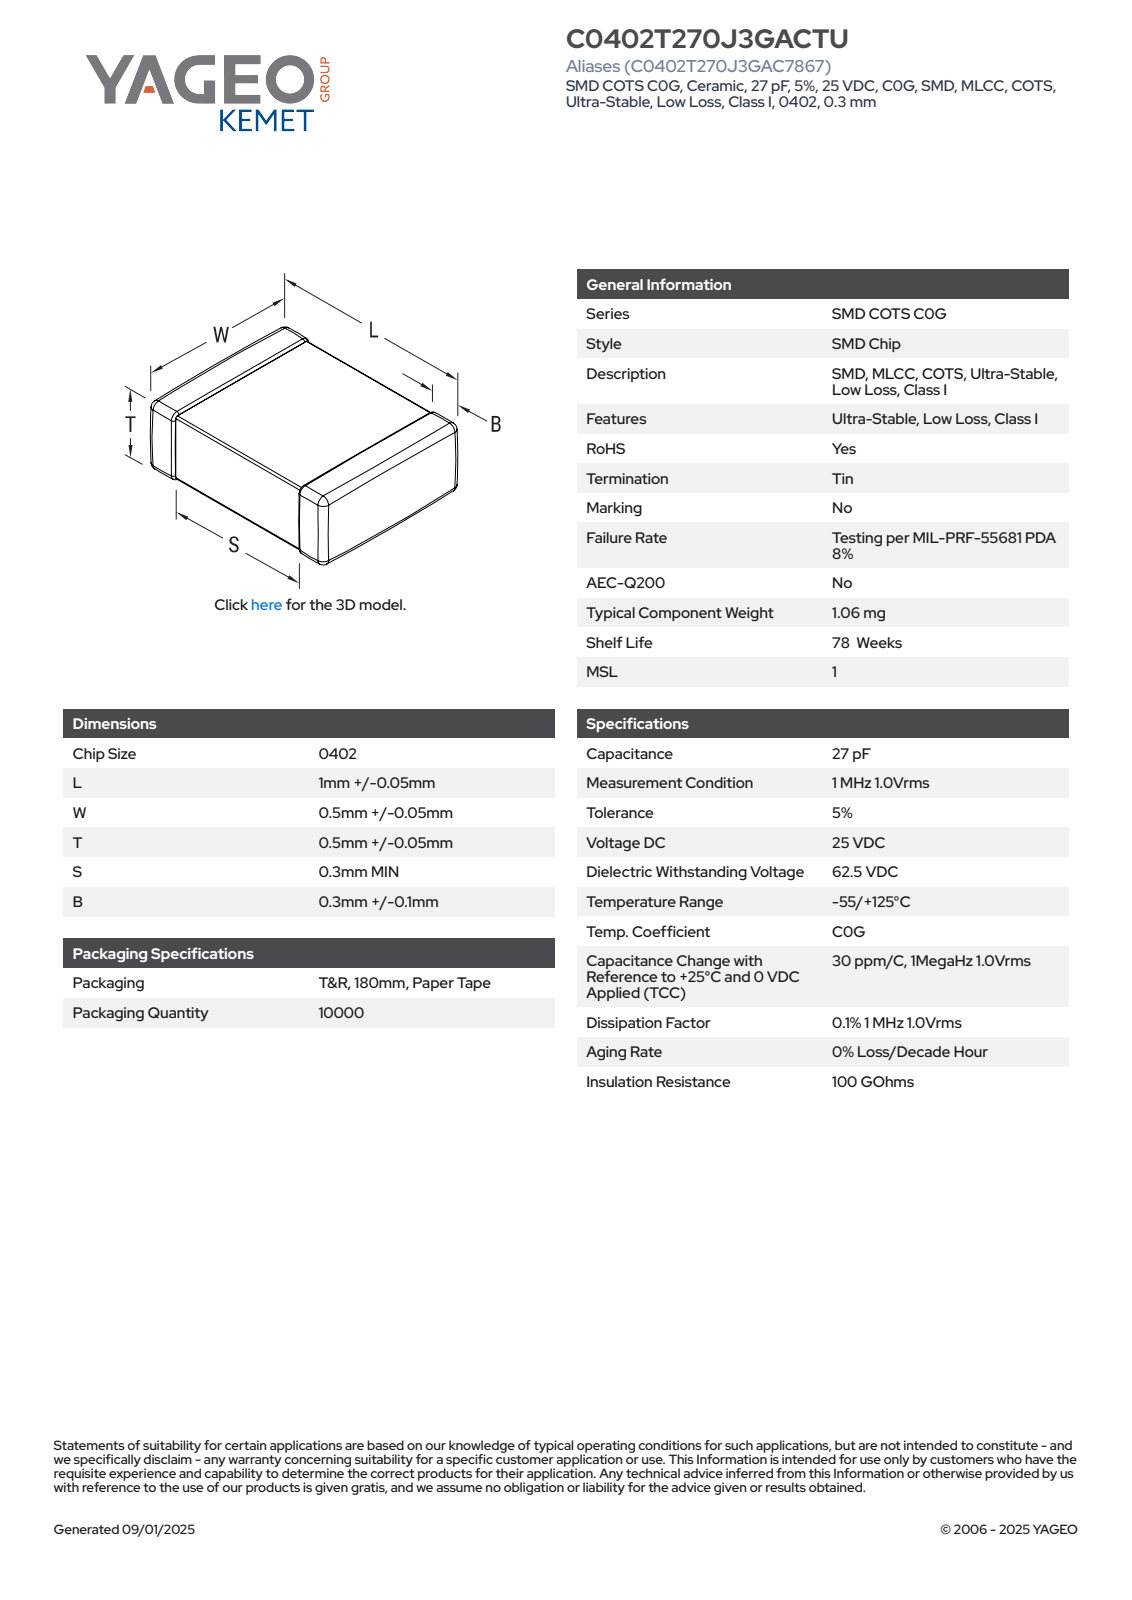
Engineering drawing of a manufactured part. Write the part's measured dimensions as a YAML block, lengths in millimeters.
part_name: "CCSM_STD_0402_L1.05W0.55T0.55B0.4"
step_written_by: "SolidWorks 2014 (AUTOMOTIVE_DESIGN)"
units: millimeters
bodies: {solids: 4, faces: 129, planar: 71, cylindrical: 42, other: 16}
overall_size: [1.05, 0.55, 0.55]
volume: 0.311
surface_area: 3
face_to_face_distances: [0.55, 0.54, 1.05, 0.53, 0.31, 0.32]
